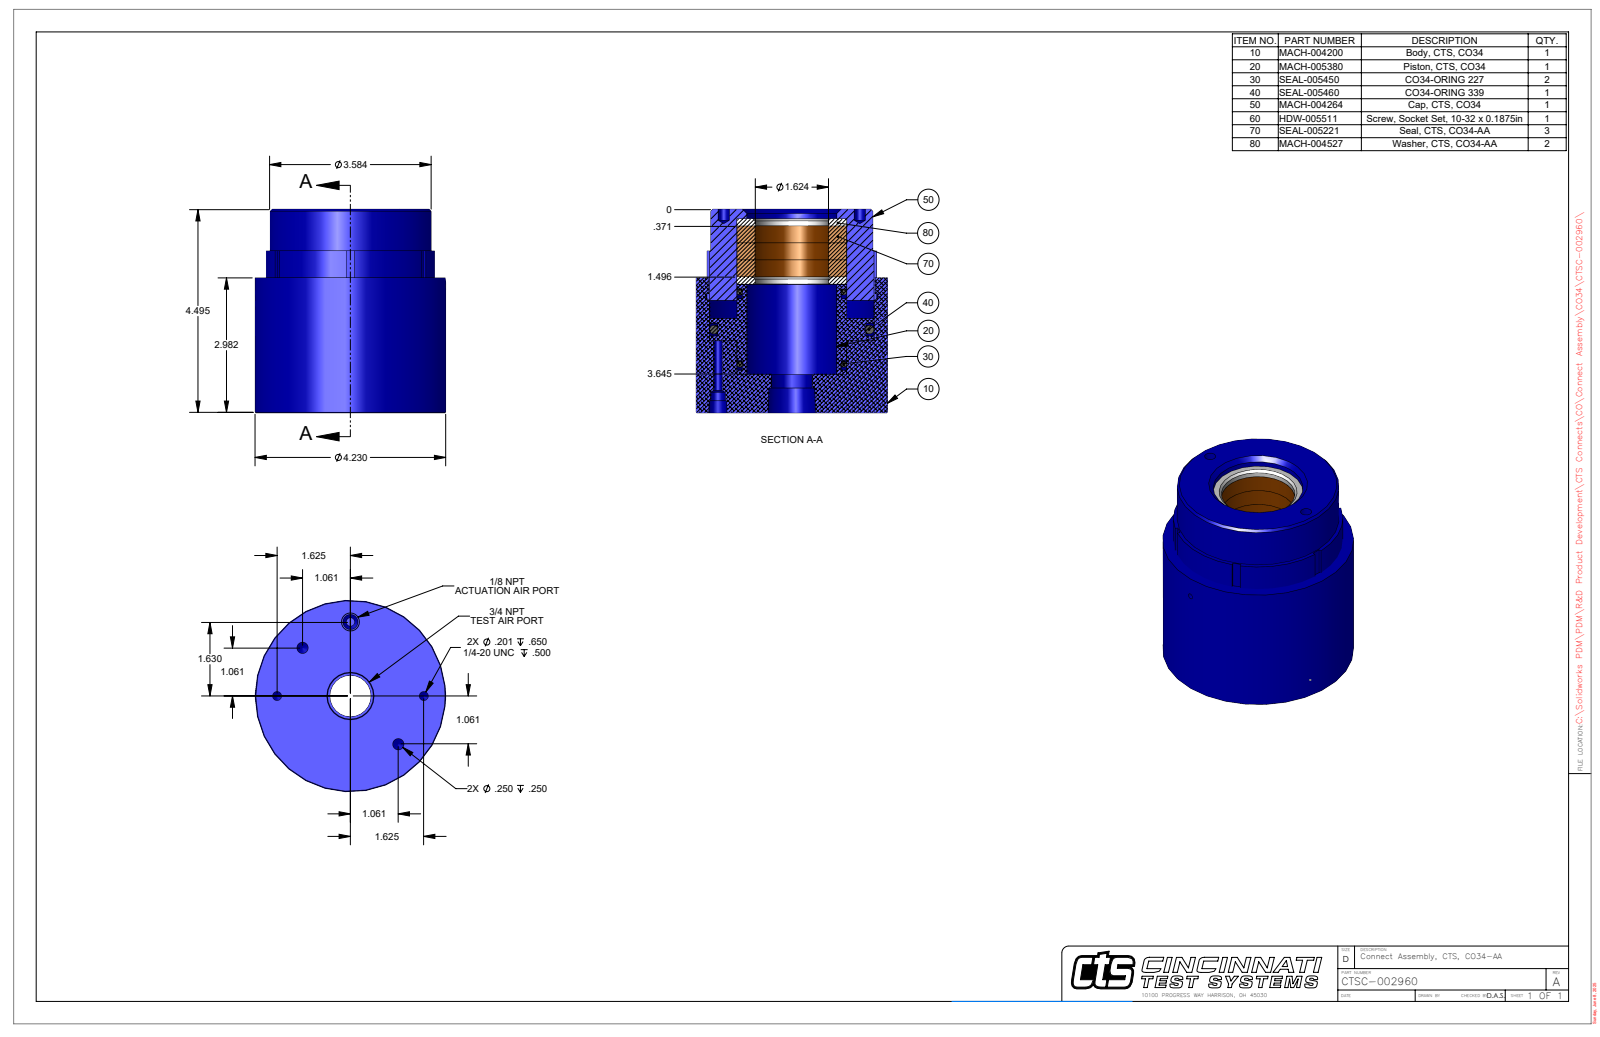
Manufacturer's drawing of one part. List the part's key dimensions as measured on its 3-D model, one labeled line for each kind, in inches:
Part name (STEP PRODUCT): CTSC-002960
STEP written by: SolidWorks 2023 (AUTOMOTIVE_DESIGN)
Units: inches
Bodies: 1 solid, 140 faces (50 planar, 62 cylindrical, 28 other)
Overall size (bounding box): 4.495 × 4.231 × 4.23
Volume: 46.9 in³ · Surface area: 136.9 in²
Round holes (diameter × count): ⌀0.25 ×4, ⌀0.201 ×2, ⌀0.125 ×1, ⌀0.159 ×1, ⌀0.187 ×1, ⌀0.332 ×1, ⌀0.906 ×1, ⌀1.624 ×1, ⌀1.626 ×1, ⌀1.987 ×1, ⌀1.988 ×1, ⌀2.427 ×1
Round bosses / shafts (diameter × count): ⌀4.23 ×1, ⌀3.75 ×1, ⌀3.584 ×1, ⌀2.417 ×1, ⌀2.416 ×1, ⌀2.412 ×1
Partial cylindrical surfaces — rounded edges, fillets, slot ends (radius × count): R1.844 ×1, R2.066 ×1
Main face-to-face distances: 4.495, 2.982, 1.513, 2.843, 0.139, 1.652, 0.85, 1.993, 2.132, 3.645
Hole centre spacings: 1.5, 2.211, 1.148, 1.201, 1.625, 2.302, 2.772, 2.887
